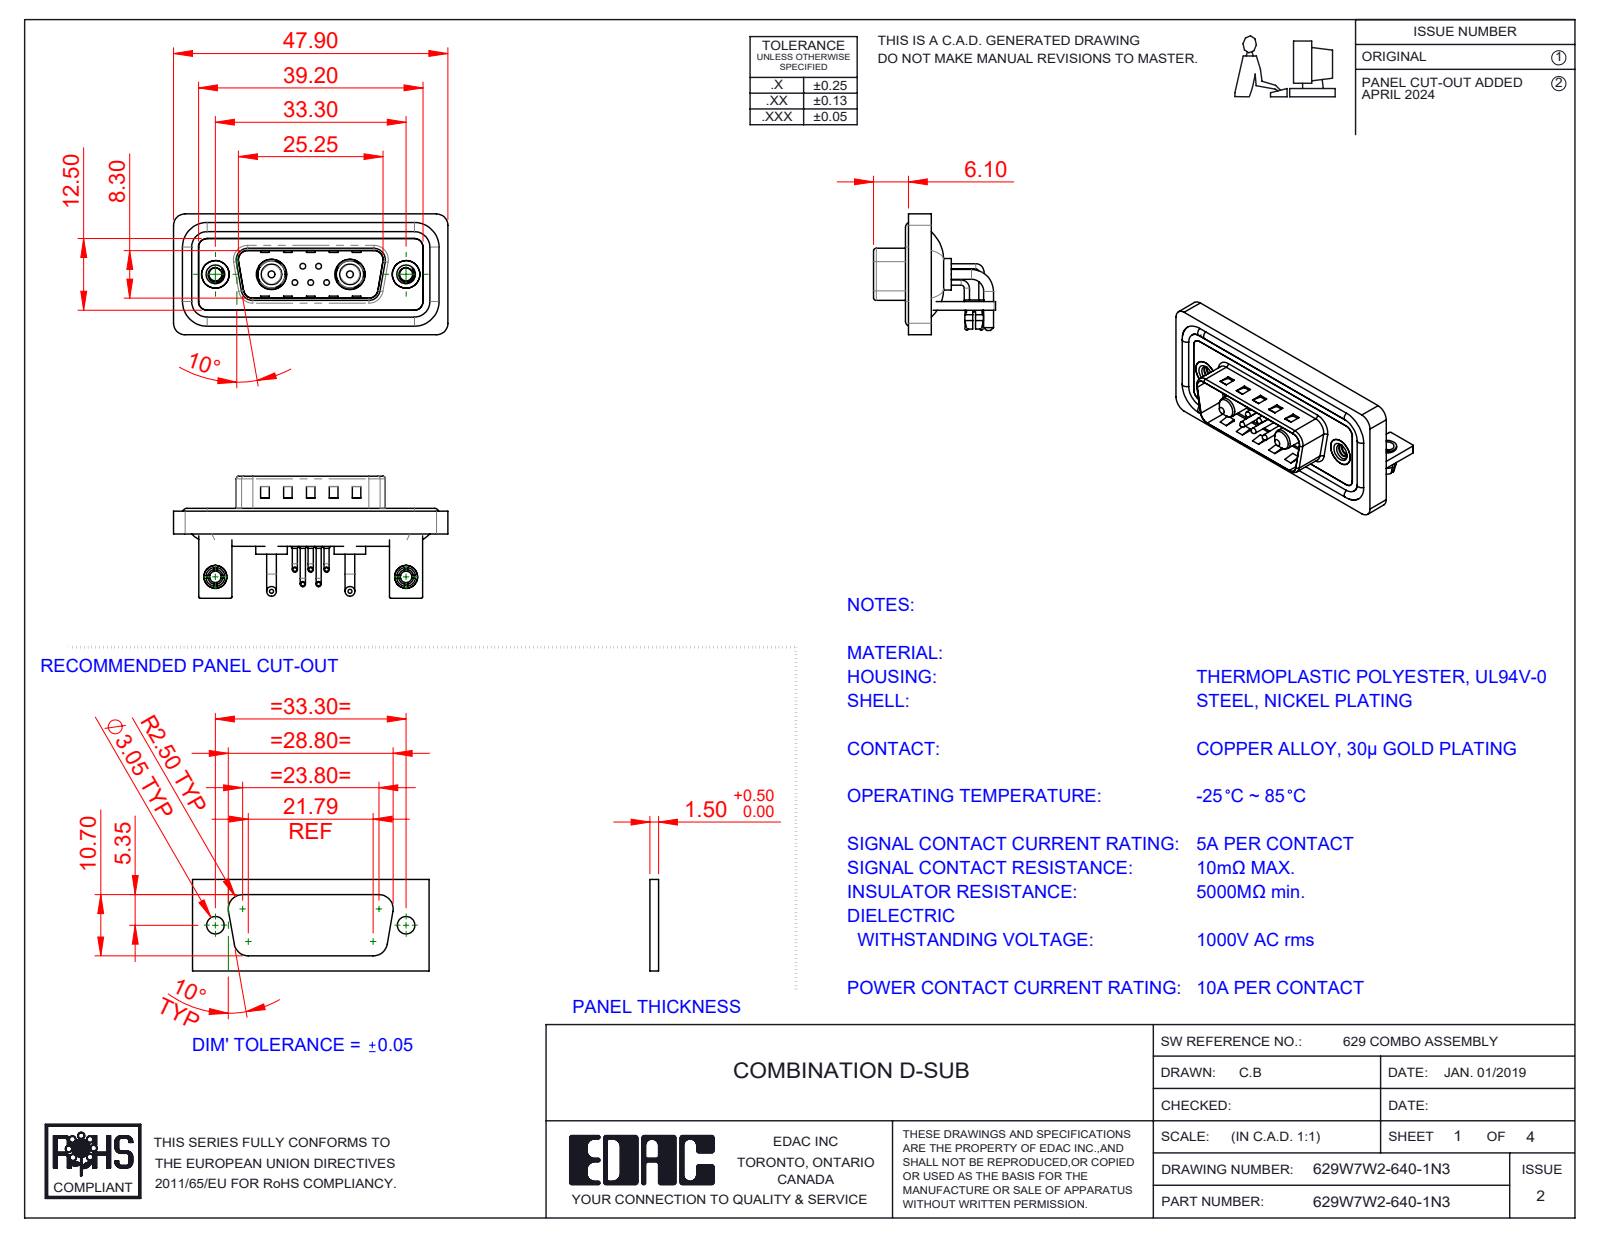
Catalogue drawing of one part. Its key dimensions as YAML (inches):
part_name: "629Combo Waterproof Housing_15 Contacts; 629Combo Shell Front_15 Contacts; 629Combo Contact Row 2; 629Combo Housing_7W2 (+7 more)"
step_written_by: "SolidWorks 2023 (CONFIG_CONTROL_DESIGN)"
units: inches
bodies: {solids: 20, faces: 1215, planar: 585, cylindrical: 456, other: 174}
overall_size: [1.886, 0.839, 0.831]
volume: 0.359
surface_area: 15.25
round_holes:
  - {diameter: 0.079, count: 7}
  - {diameter: 0.03, count: 5}
  - {diameter: 0.063, count: 5}
  - {diameter: 0.089, count: 2}
  - {diameter: 0.098, count: 2}
  - {diameter: 0.126, count: 2}
  - {diameter: 0.157, count: 2}
  - {diameter: 0.189, count: 2}
  - {diameter: 0.191, count: 2}
  - {diameter: 0.197, count: 2}
  - {diameter: 0.209, count: 2}
round_bosses_or_shafts:
  - {diameter: 0.035, count: 10}
  - {diameter: 0.059, count: 5}
  - {diameter: 0.039, count: 5}
  - {diameter: 0.026, count: 5}
  - {diameter: 0.067, count: 4}
  - {diameter: 0.063, count: 4}
  - {diameter: 0.217, count: 2}
  - {diameter: 0.205, count: 2}
partial_cylinders:
  - {radius: 0.079, count: 21}
  - {radius: 0.059, count: 18}
  - {radius: 0.01, count: 16}
  - {radius: 0.02, count: 9}
  - {radius: 0.063, count: 8}
  - {radius: 0.04, count: 5}
  - {radius: 0.024, count: 4}
  - {radius: 0.026, count: 4}
face_to_face_distances: [0.016, 0.059, 0.031, 0.114, 0.083, 0.043, 0.063, 0.047, 0.146, 0.177]
hole_center_spacings: [0.124, 0.109, 0.386, 0.925, 1.311, 0.17, 0.17, 0.198]
